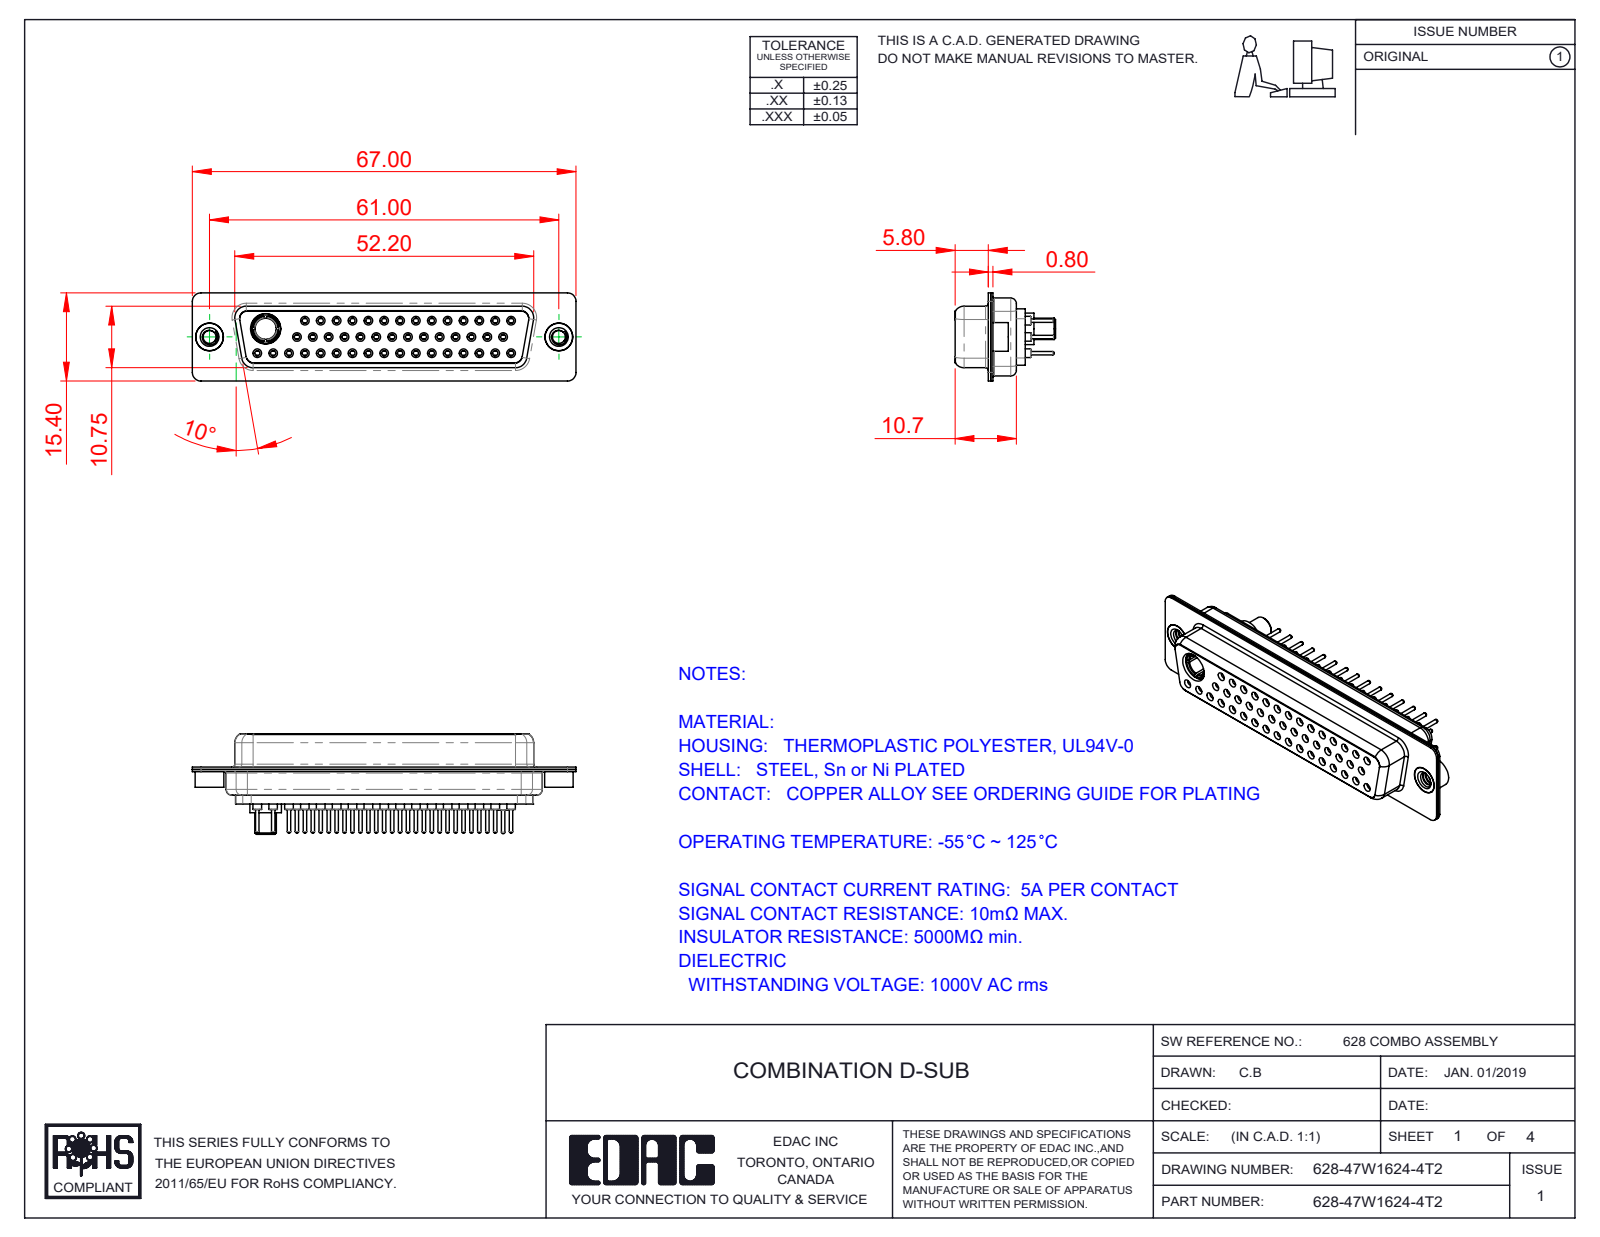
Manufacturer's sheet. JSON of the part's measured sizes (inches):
{"part_name": "Power Socket_40A S; 628-47W1624-4T2; 628Combo Housing_47W1; 628Combo Contact Row 3_24 (+5 more)", "step_written_by": "SolidWorks 2016 (CONFIG_CONTROL_DESIGN)", "units": "inches", "bodies": {"solids": 53, "faces": 2871, "planar": 783, "cylindrical": 1026, "other": 1062}, "overall_size": [2.638, 0.691, 0.606], "volume_in3": 0.434, "surface_area_in2": 22.79, "round_holes": [[0.043, 46], [0.035, 45], [0.059, 45], [0.079, 45], [0.063, 31], [0.067, 14], [0.191, 3], [0.089, 2], [0.157, 2], [0.159, 2], [0.146, 1], [0.209, 1]], "round_bosses_or_shafts": [[0.087, 46], [0.024, 46], [0.063, 15], [0.197, 2], [0.195, 2], [0.189, 2], [0.217, 1], [0.205, 1]], "partial_cylinders_radius": [[0.059, 16], [0.053, 12], [0.079, 12], [0.063, 8], [0.01, 4], [0.02, 4], [0.024, 4], [0.026, 4]], "face_to_face_distances": [0.016, 0.446, 0.254, 0.238, 0.074, 0.482, 0.244, 0.228, 0.407, 0.43], "hole_center_spacings": [0.124, 0.109, 0.218, 0.327, 0.436, 0.545, 0.654, 0.763]}
